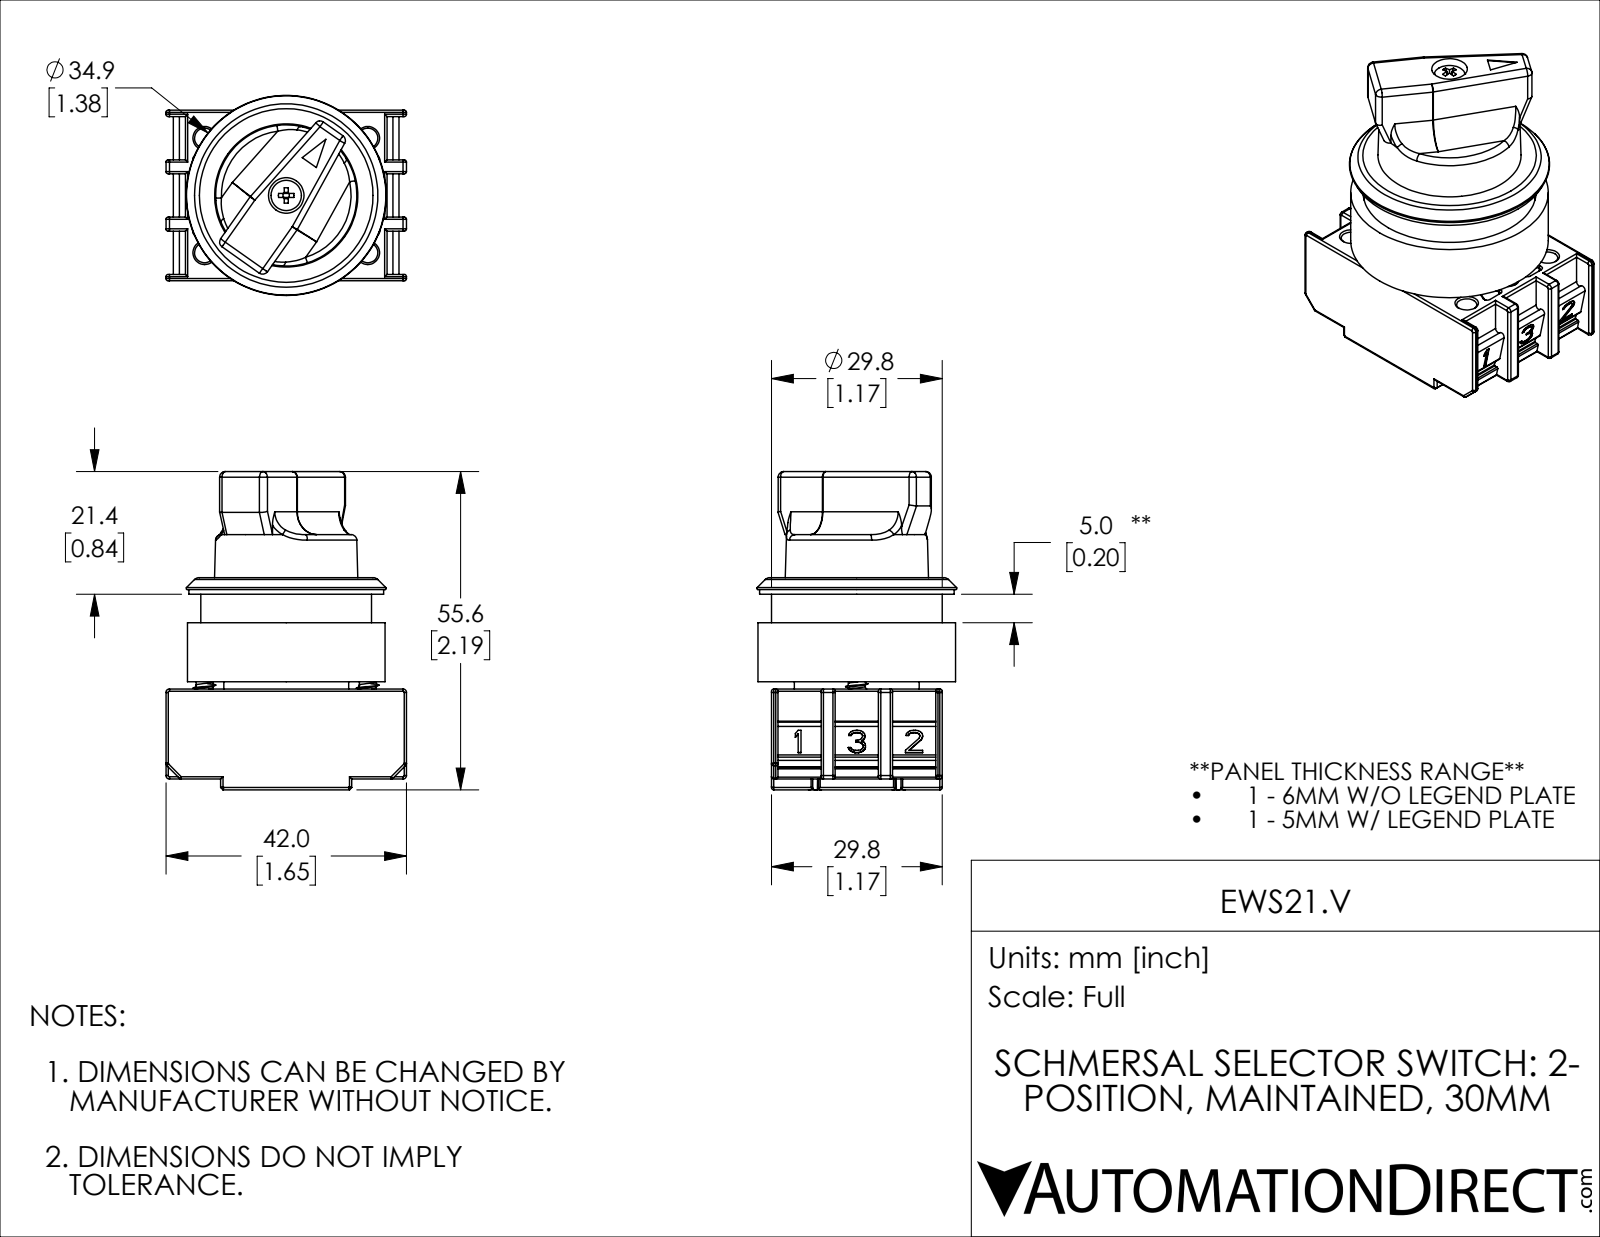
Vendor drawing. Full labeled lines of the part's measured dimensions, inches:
Part name (STEP PRODUCT): EWS21.V
STEP written by: SolidWorks 2019 (CONFIG_CONTROL_DESIGN)
Units: inches
Bodies: 5 solids, 1635 faces (619 planar, 557 cylindrical, 459 other)
Overall size (bounding box): 2.187 × 1.654 × 1.375
Volume: 1.789 in³ · Surface area: 39.07 in²
Round holes (diameter × count): ⌀0.138 ×6, ⌀0.203 ×6, ⌀0.244 ×1, ⌀0.36 ×1, ⌀0.39 ×1, ⌀0.433 ×1, ⌀0.551 ×1, ⌀0.748 ×1, ⌀0.866 ×1, ⌀0.953 ×1, ⌀1.024 ×1, ⌀1.189 ×1
Round bosses / shafts (diameter × count): ⌀0.189 ×2, ⌀0.115 ×2, ⌀1.358 ×1, ⌀1.339 ×1, ⌀1.173 ×1, ⌀1.004 ×1, ⌀0.858 ×1, ⌀0.728 ×1
Partial cylindrical surfaces — rounded edges, fillets, slot ends (radius × count): R0.016 ×110, R0.012 ×48, R0.039 ×30, R0.008 ×26, R0.02 ×16, R0.024 ×8, R0.031 ×6, R0.157 ×4
Main face-to-face distances: 0.634, 0.683, 0.742, 1.173, 0.165, 0.886, 0.555, 1.459, 0.717, 0.075
Hole centre spacings: 0.394, 0.685, 1.189, 1.122, 0.561, 0.787, 1.371
